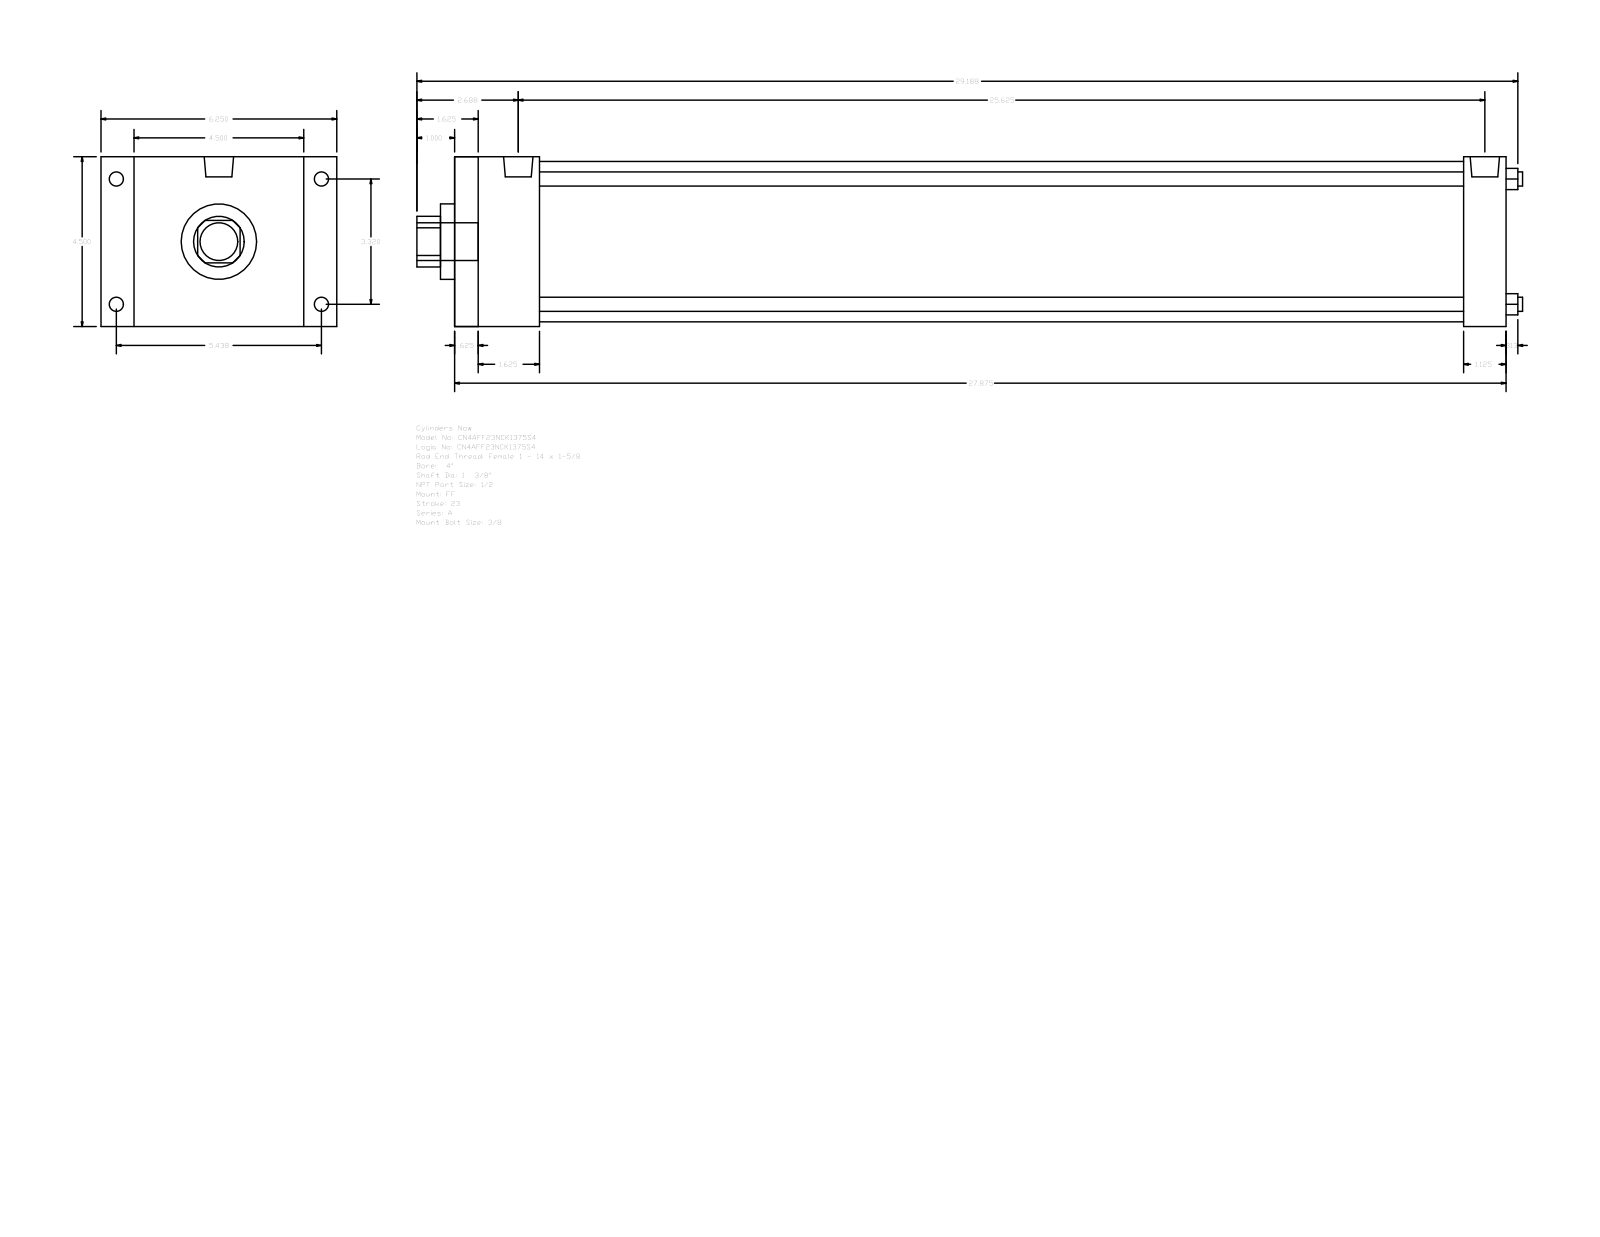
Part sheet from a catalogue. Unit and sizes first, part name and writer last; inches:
Units: inches
Overall size (bounding box): 29.313 × 6.25 × 4.5
Round holes (diameter × count): ⌀0.375 ×4, ⌀1.375 ×1, ⌀2 ×1, ⌀4.25 ×1
Round bosses / shafts (diameter × count): ⌀0.375 ×4, ⌀0.344 ×4, ⌀0.778 ×2, ⌀1 ×1
Partial cylindrical surfaces — rounded edges, fillets, slot ends (radius × count): R0.672 ×1
Main face-to-face distances: 4.5, 27.875, 27.25, 0.625, 1.125, 0.875, 5.375, 26.75, 26.125, 2.25
Hole centre spacings: 2.347, 3.32, 4.695
Bodies: 0 solids, 92 faces (64 planar, 28 cylindrical, 0 other)
Part name (STEP PRODUCT): A_FF__0400_1.375
STEP written by: GSSL Pune (CONFIG_CONTROL_DESIGN)
